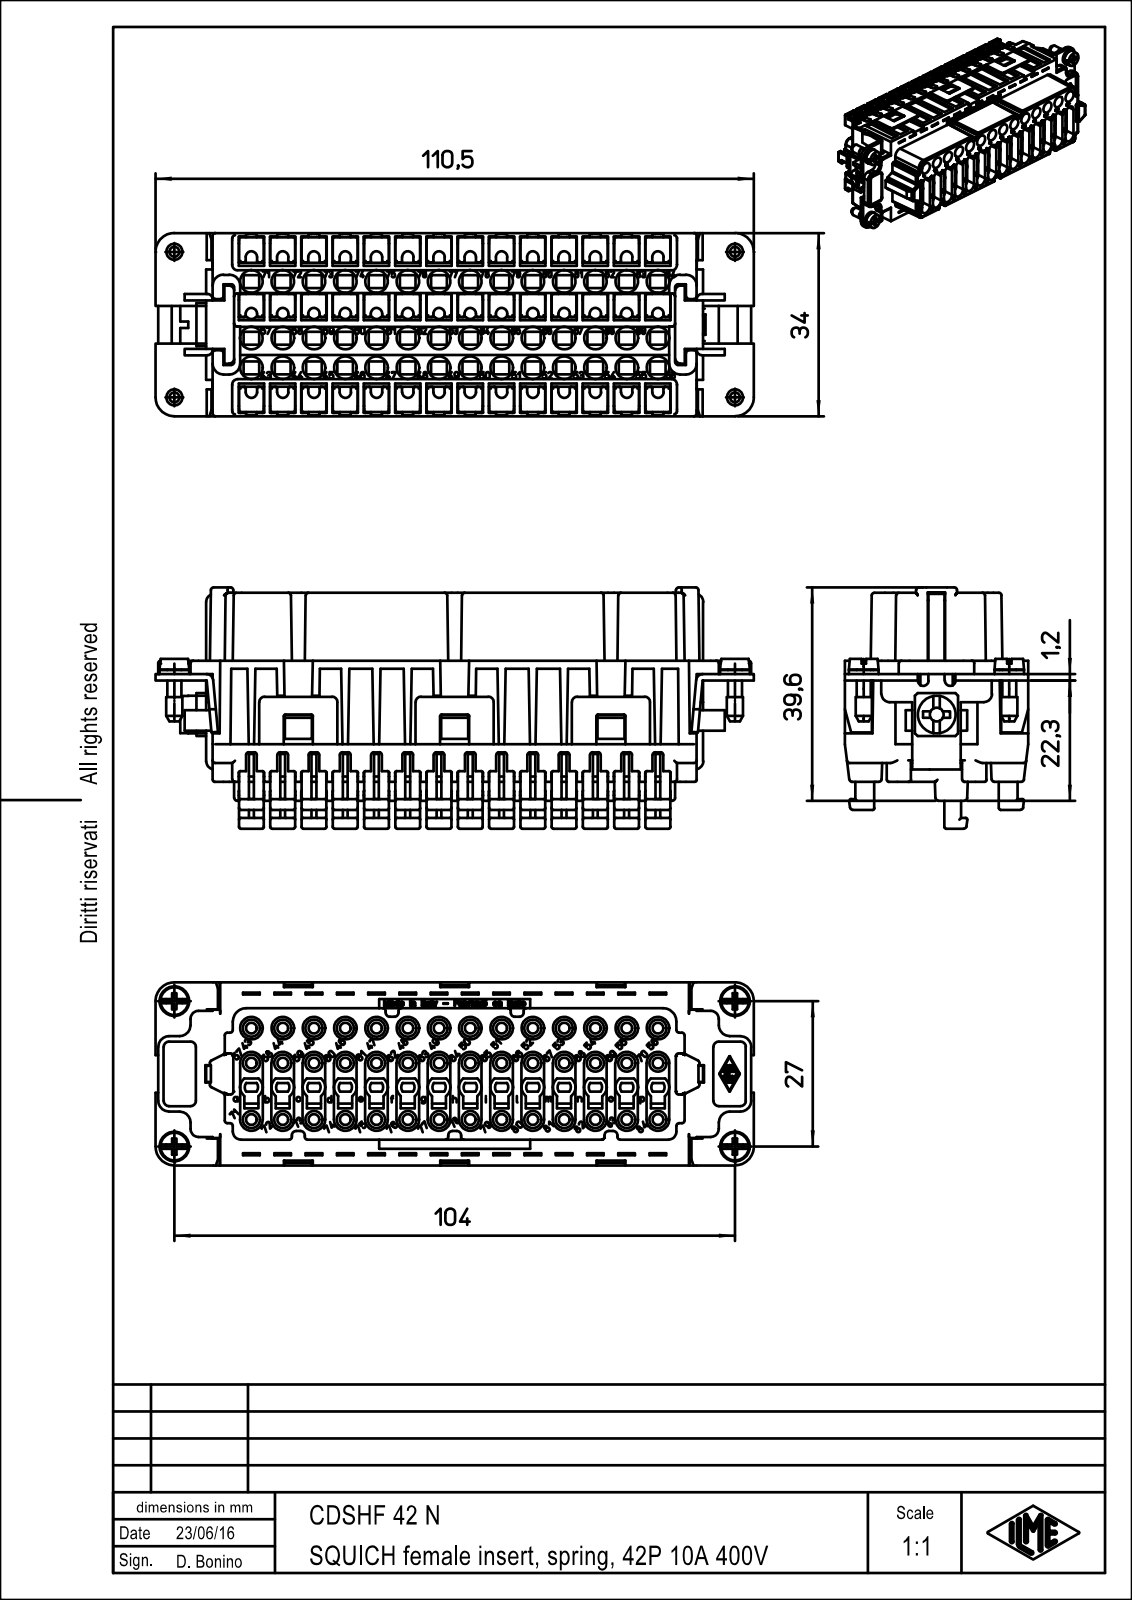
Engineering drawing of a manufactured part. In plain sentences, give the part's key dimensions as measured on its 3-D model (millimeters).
The part is named "CDSHF_42_N". Its 3-D file was written by "PTC Creo Elements/Direct Modeling 19.0B 21-Mar-2015 (C) Parametric Technology GmbH (AUTOMOTIVE_DESIGN)". It is 1 solid with 2197 faces: 1847 planar, 342 cylindrical and 8 other. Overall it measures 111 by 44.8 by 34 millimeters. Its volume is 90 292 cubic millimeters and its surface area 31 542 square millimeters. Round holes: 56 of diameter 4.2, 42 of diameter 2, 1 of diameter 4. Round bosses or shafts: 4 of diameter 5.5, 4 of diameter 3, 1 of diameter 7. Partial cylindrical surfaces (rounded edges, fillets, slot ends): 42 of radius 1.05, 42 of radius 2.1, 8 of radius 1.5, 8 of radius 2, 4 of radius 3.5, 2 of radius 1, 2 of radius 2.5. The main face-to-face distances are 3.5, 29.2, 4.8, 1.2, 34, 7, 1, 10.5, 24.4, 16.5. The hole center spacings are 5.8, 7.99, 11.6, 12.84, 17.4, 18.25, 23.2, 23.84.
